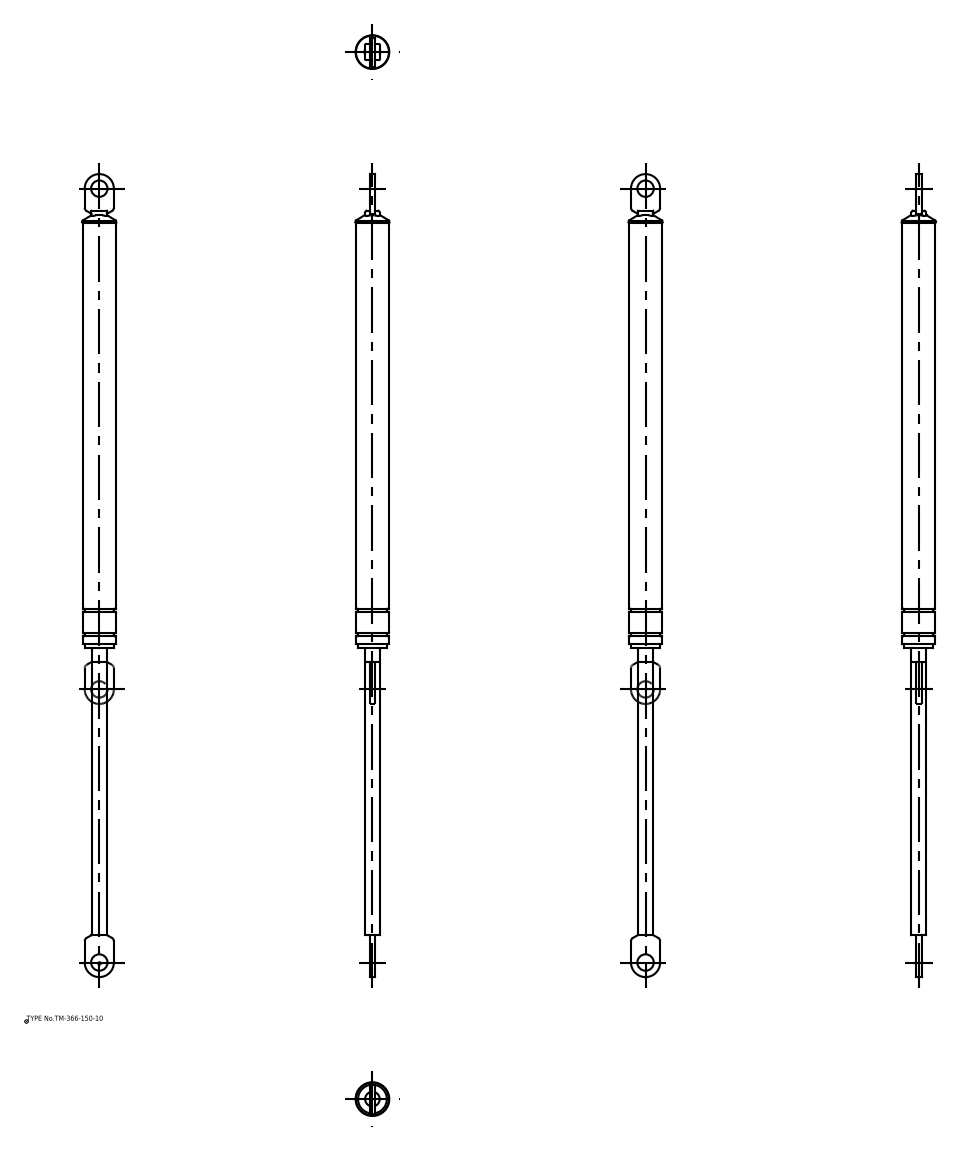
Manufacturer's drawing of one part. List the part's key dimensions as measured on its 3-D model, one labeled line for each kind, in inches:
Part name (STEP PRODUCT): TM_366_150_10; TM_366_150_10_div
STEP written by: spGate 16.7.1 (AUTOMOTIVE_DESIGN)
Units: inches
Bodies: 2 solids, 89 faces (35 planar, 36 cylindrical, 18 other)
Overall size (bounding box): 17.362 × 0.728 × 0.728
Volume: 4.245 in³ · Surface area: 30.37 in²
Round holes (diameter × count): ⌀0.354 ×2
Round bosses / shafts (diameter × count): ⌀0.709 ×1, ⌀0.622 ×1, ⌀0.315 ×1
Partial cylindrical surfaces — rounded edges, fillets, slot ends (radius × count): R0.012 ×8, R0.079 ×4, R0.02 ×2, R0.045 ×2, R0.315 ×2
Main face-to-face distances: 0.126, 0.63, 0.067, 6.22, 6.287, 0.146, 0.484, 0.531, 0.071, 0.094
Hole centre spacings: 16.732
